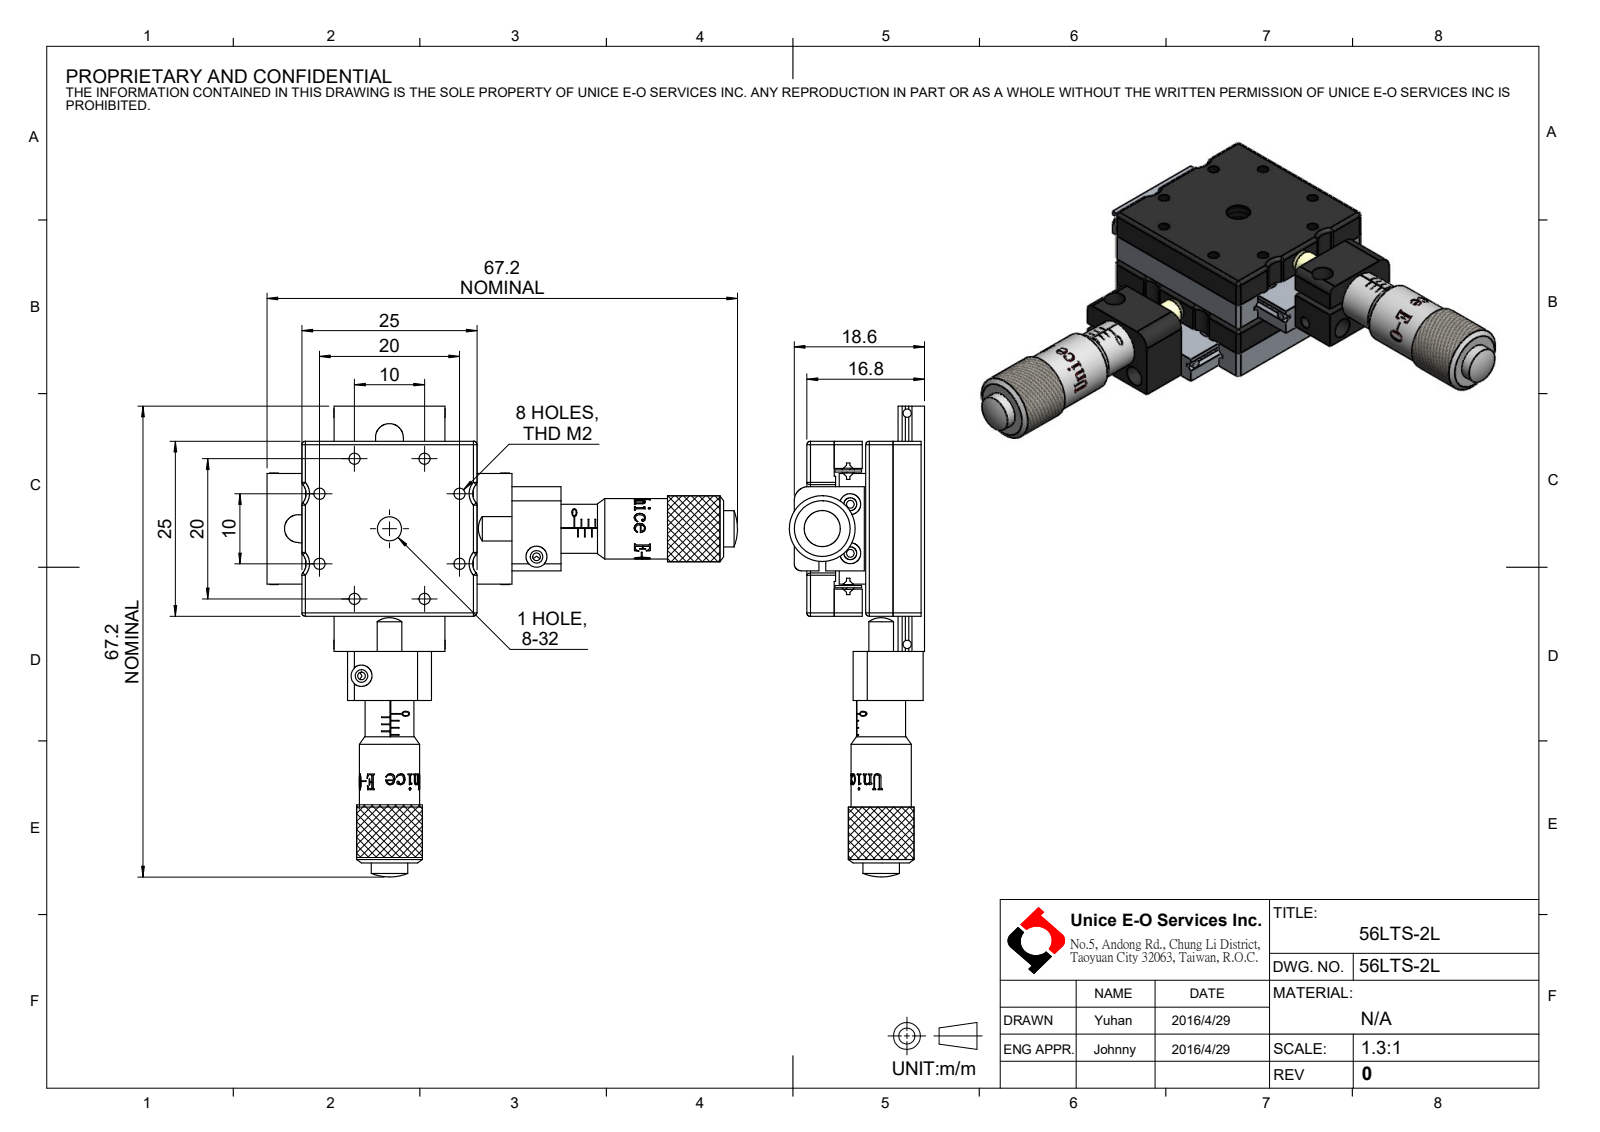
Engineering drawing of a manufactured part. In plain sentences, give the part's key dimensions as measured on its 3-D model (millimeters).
The part is named "56LTS-2L". Its 3-D file was written by "SolidWorks 2016 (CONFIG_CONTROL_DESIGN)". It is 42 solids with 1664 faces: 666 planar, 622 cylindrical and 376 other. Overall it measures 67.2 by 67.2 by 19.3 millimeters. Its volume is 13 396 cubic millimeters and its surface area 16 109 square millimeters. Round holes: 20 of diameter 1.1, 18 of diameter 1.8, 12 of diameter 3.1, 8 of diameter 1.2, 8 of diameter 1.6, 8 of diameter 2.4, 8 of diameter 3, 8 of diameter 4, 2 of diameter 1.7, 2 of diameter 2.5, 2 of diameter 2.6, 2 of diameter 3.5. Round bosses or shafts: 21 of diameter 1.5, 2 of diameter 9.4, 2 of diameter 8.6, 2 of diameter 7, 2 of diameter 6.4, 2 of diameter 5.7, 2 of diameter 5.2, 2 of diameter 1.2. Partial cylindrical surfaces (rounded edges, fillets, slot ends): 28 of radius 0.5, 14 of radius 0.75, 14 of radius 2, 2 of radius 1, 2 of radius 4.28. The main face-to-face distances are 8.4, 4.6, 3.8, 0.7, 3.9, 0.5, 4.3, 4.1, 4.5, 8.9. The hole center spacings are 4.04, 5.03, 5.64, 9, 10.66, 11.18, 11.44, 13.87.
